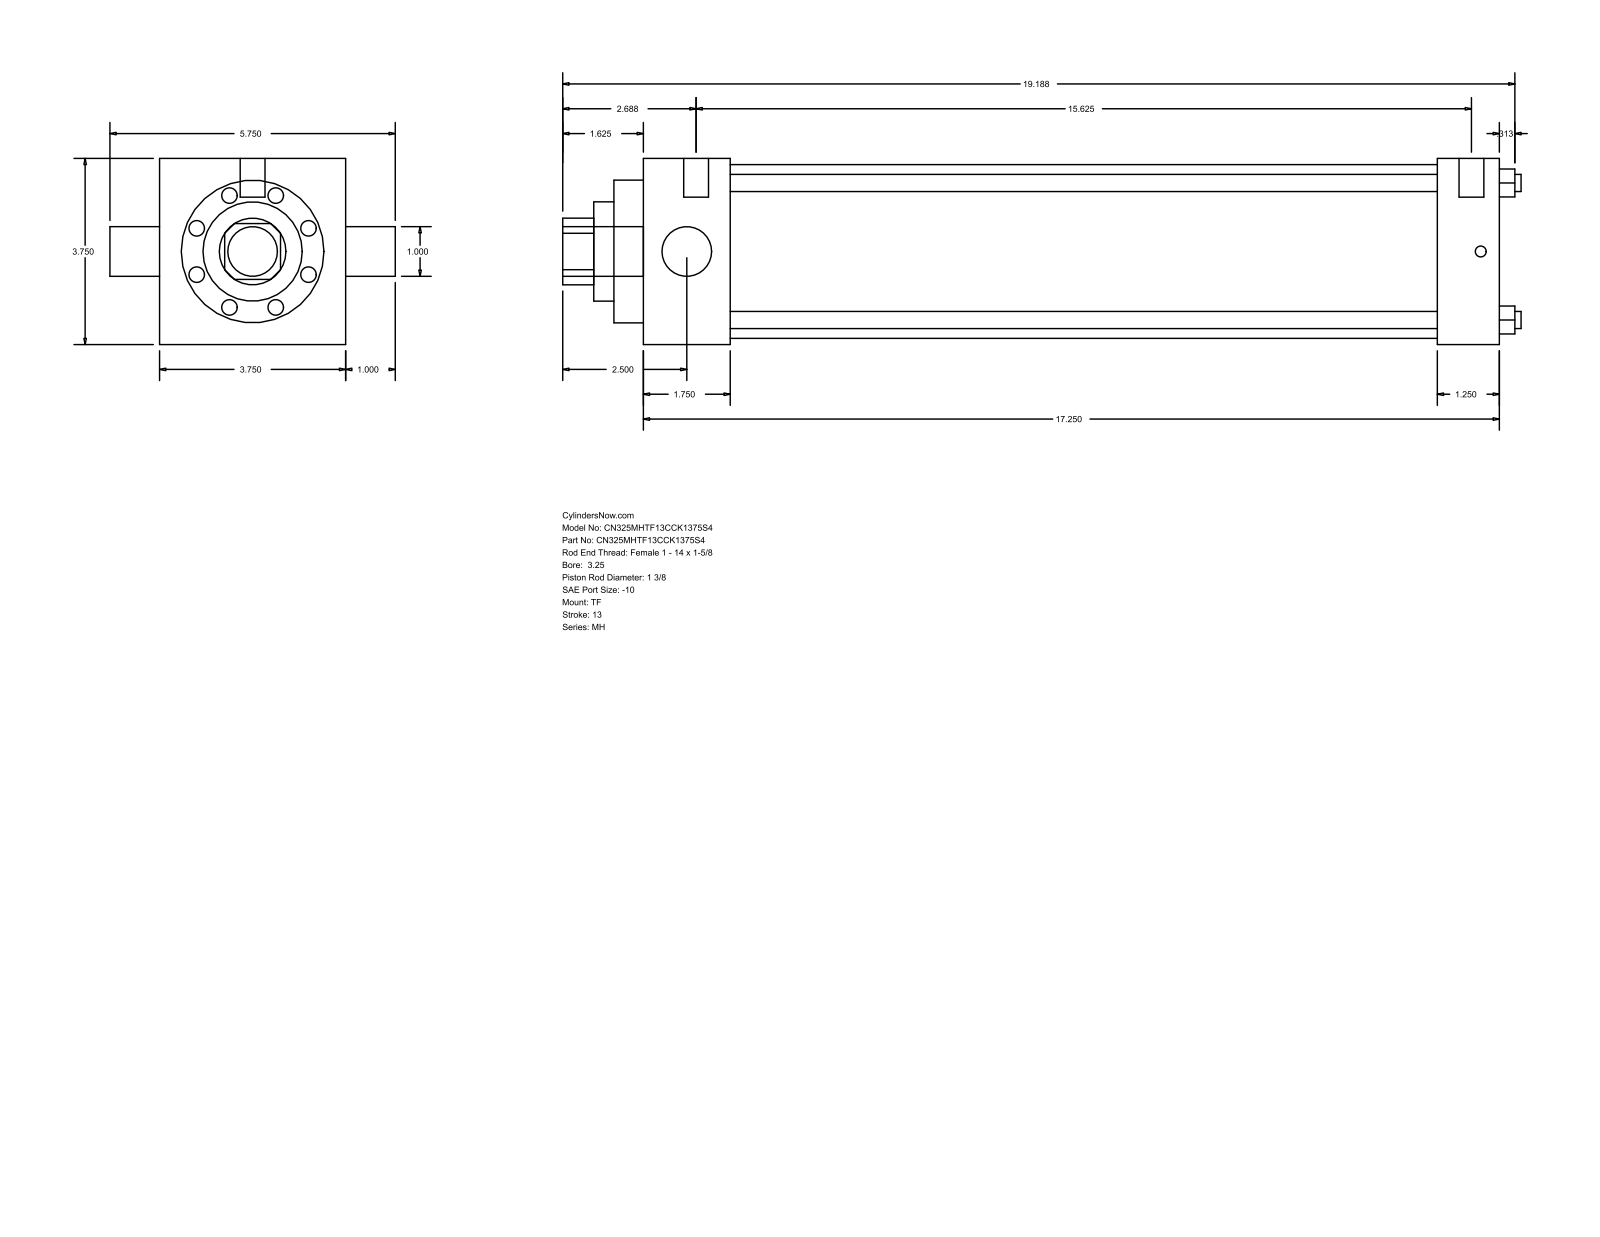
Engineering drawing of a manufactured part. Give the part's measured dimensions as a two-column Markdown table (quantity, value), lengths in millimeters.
| quantity | value |
| --- | --- |
| part name | MH_TF__0325_1.375 |
| STEP written by | GSSL Pune (CONFIG_CONTROL_DESIGN) |
| units | millimeters |
| bodies | 0 solids, 86 faces (61 planar, 25 cylindrical, 0 other) |
| overall size | 490.54 × 146.05 × 95.25 |
| round holes (diameter × count) | 8.76 × 4, 25.4 × 1, 34.92 × 1, 50.8 × 1, 73.03 × 1, 88.9 × 1 |
| round bosses / shafts (diameter × count) | 5.56 × 3, 12.7 × 2, 25.4 × 1 |
| partial cylindrical surfaces (radius × count) | 17.06 × 1 |
| main face-to-face distances | 95.24, 438.16, 44.45, 406.41, 361.96, 393.71, 31.75, 15.08, 59.53, 421.49 |
| hole center spacings | 49.57, 70.1, 99.14 |
